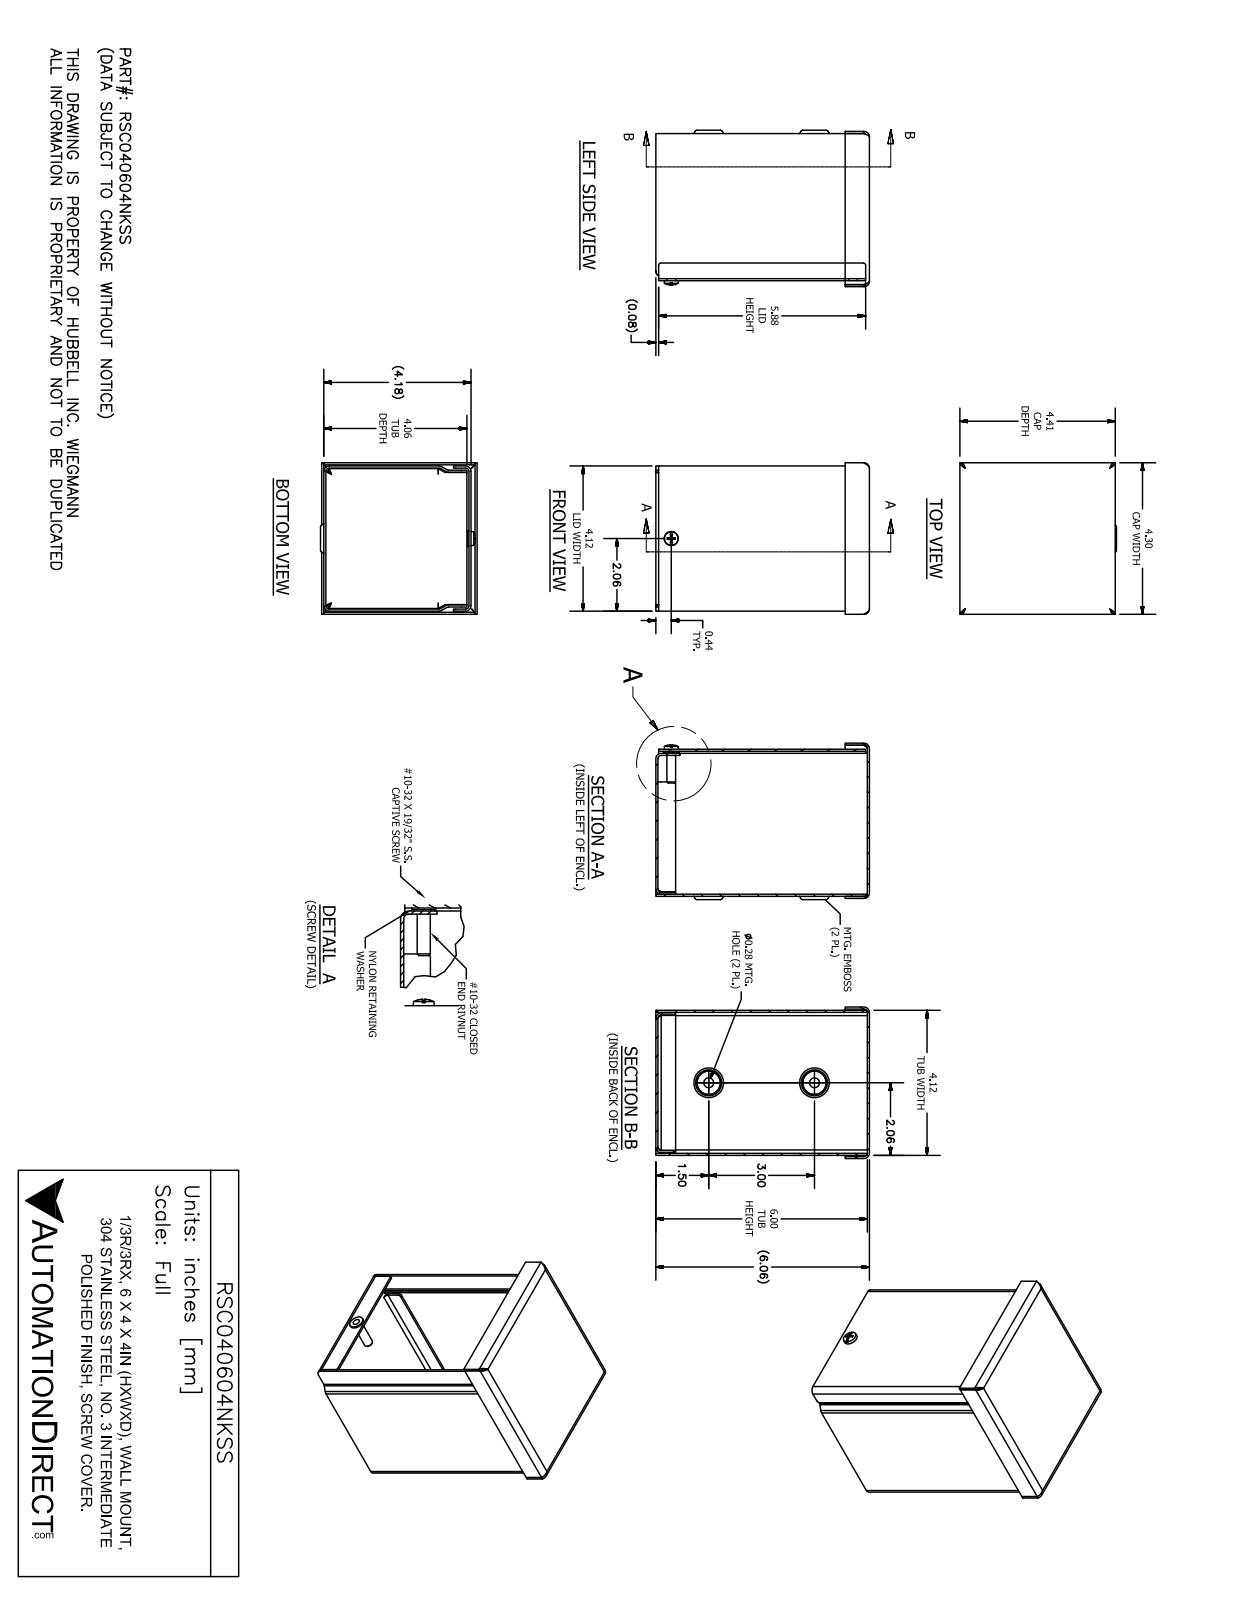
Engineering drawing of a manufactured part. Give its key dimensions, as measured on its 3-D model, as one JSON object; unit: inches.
{"part_name": "RSC040604NKSS", "step_written_by": "SolidWorks 2017 (AUTOMOTIVE_DESIGN)", "units": "inches", "bodies": {"solids": 7, "faces": 231, "planar": 124, "cylindrical": 58, "other": 49}, "overall_size": [6.059, 4.441, 4.299], "volume_in3": 9.042, "surface_area_in2": 313.1, "round_holes": [[0.25, 2], [0.281, 2], [0.156, 1], [0.196, 1], [0.257, 1], [0.278, 1]], "round_bosses_or_shafts": [[0.453, 1], [0.406, 1], [0.248, 1], [0.167, 1]], "partial_cylinders_radius": [[0.094, 16], [0.153, 16], [0.031, 2], [0.062, 2], [0.063, 2], [0.089, 1], [0.156, 1]], "face_to_face_distances": [0.059, 4.059, 4.117, 6, 4, 4.176, 4.118, 4.058, 6.059, 5.941], "hole_center_spacings": [1.063, 1.094, 3, 4.063, 4.094, 5.156]}
